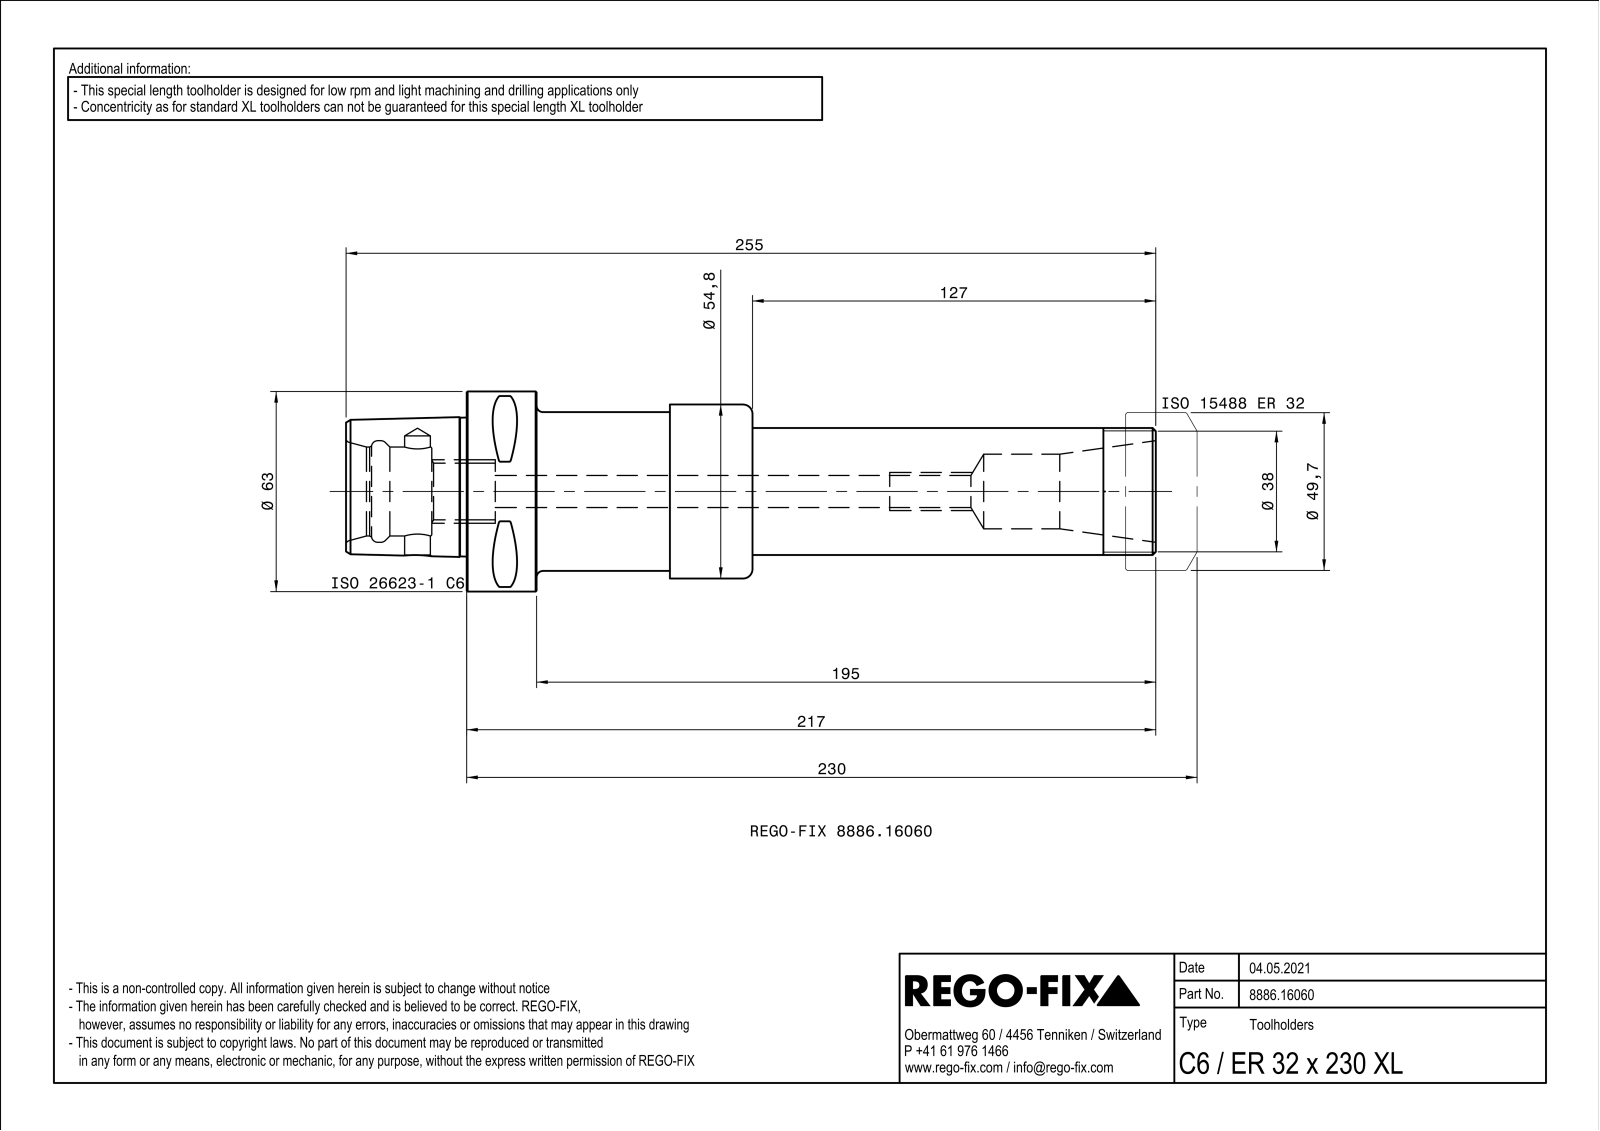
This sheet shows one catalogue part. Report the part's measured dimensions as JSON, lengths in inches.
{"part_name": "NOCUT", "step_written_by": "SIEMENS PLM Software Solid Edge ST10 (AUTOMOTIVE_DESIGN)", "units": "inches", "bodies": {"solids": 1, "faces": 155, "planar": 30, "cylindrical": 33, "other": 92}, "overall_size": [10.039, 2.48, 2.48], "volume_in3": 21, "surface_area_in2": 104.8, "round_holes": [[0.157, 1], [0.319, 1], [0.398, 1], [0.398, 1], [0.512, 1], [0.702, 1], [0.925, 1], [1.102, 1], [1.26, 1], [1.299, 1], [1.583, 1], [1.905, 1]], "round_bosses_or_shafts": [[2.48, 1], [2.157, 1], [1.969, 1], [1.772, 1], [1.654, 1], [1.575, 1], [1.244, 1], [1.201, 1]], "partial_cylinders_radius": [[0.02, 8]], "face_to_face_distances": [2.362, 0.866, 2.677, 3.543, 0.315, 3.228, 2.637, 2.323, 0.039, 0.906], "hole_center_spacings": [1.083]}
